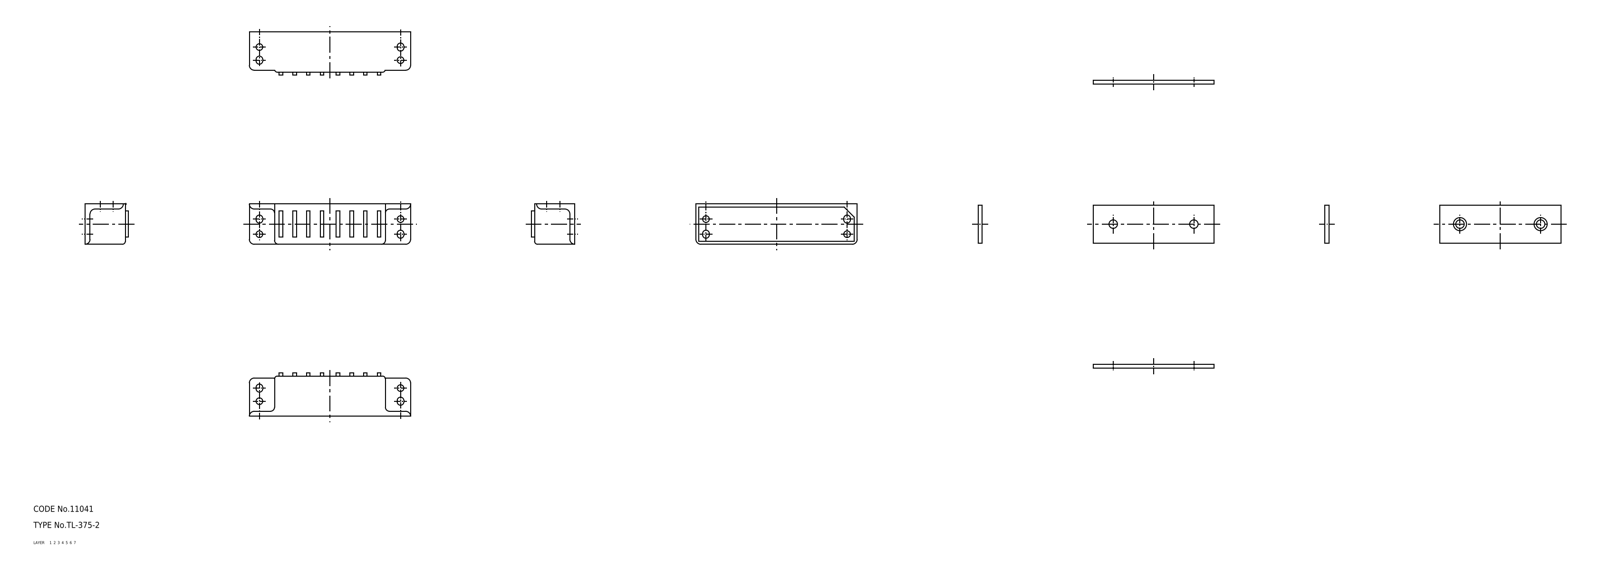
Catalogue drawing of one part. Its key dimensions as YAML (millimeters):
part_name: "67116564; 67116577; 67116590; 67116603 (+6 more)"
step_written_by: "CADfix (AUTOMOTIVE_DESIGN)"
units: millimeters
bodies: {solids: 10, faces: 187, planar: 0, cylindrical: 0, other: 187}
overall_size: [80, 47, 20]
volume: 26402
surface_area: 17685
